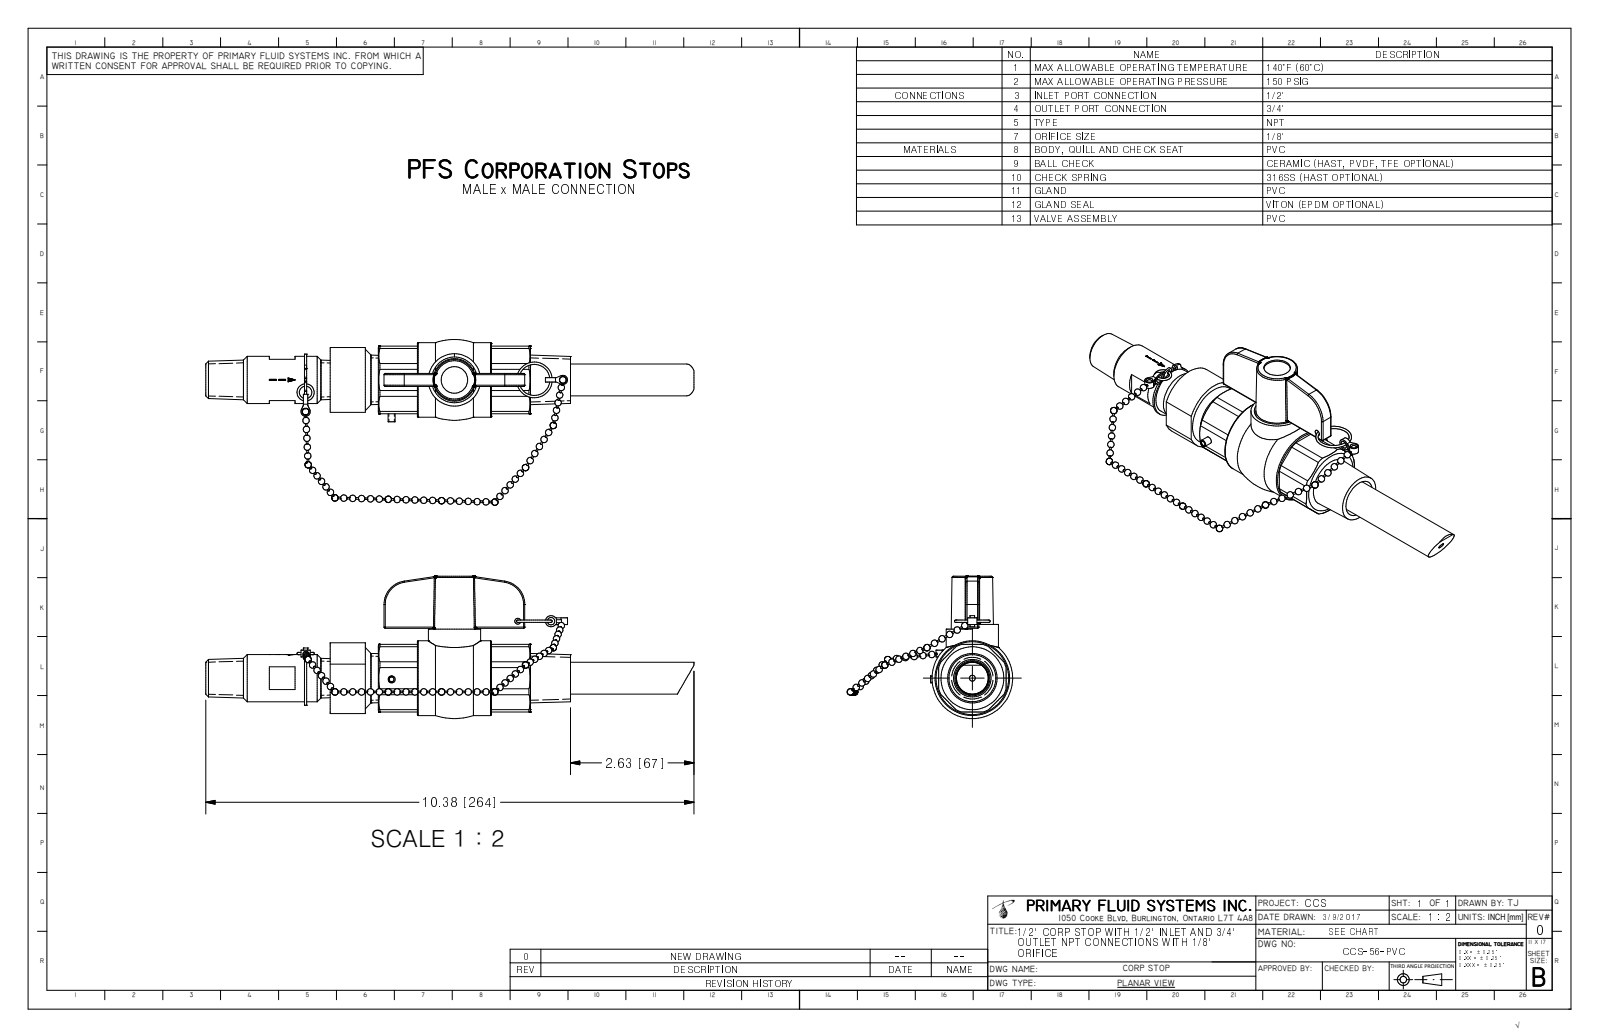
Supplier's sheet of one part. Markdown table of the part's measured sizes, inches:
| quantity | value |
| --- | --- |
| part name | CCS-56-PVC_R0 |
| STEP written by | Autodesk Inventor 2009 (AUTOMOTIVE_DESIGN) |
| units | inches |
| bodies | 1 solid, 384 faces (115 planar, 60 cylindrical, 209 other) |
| overall size | 10.38 × 3.517 × 3.016 |
| volume | 12.14 in³ |
| surface area | 64.49 in² |
| round holes (diameter × count) | 0.079 × 1, 0.125 × 1, 0.15 × 1, 0.25 × 1, 0.469 × 1, 0.56 × 1, 0.563 × 1, 0.97 × 1 |
| round bosses / shafts (diameter × count) | 1.585 × 1, 1.11 × 1, 1.094 × 1, 1 × 1, 0.9 × 1, 0.675 × 1, 0.558 × 1 |
| partial cylindrical surfaces (radius × count) | 0.025 × 12, 0.043 × 2, 0.157 × 2, 0.5 × 2, 0.451 × 1, 0.463 × 1, 0.499 × 1, 0.614 × 1 |
| main face-to-face distances | 1.435, 0.03, 0.55, 0.275, 0.825, 0.58, 0.855, 1.405, 0.25, 1.024 |
| hole center spacings | 0.535 |
